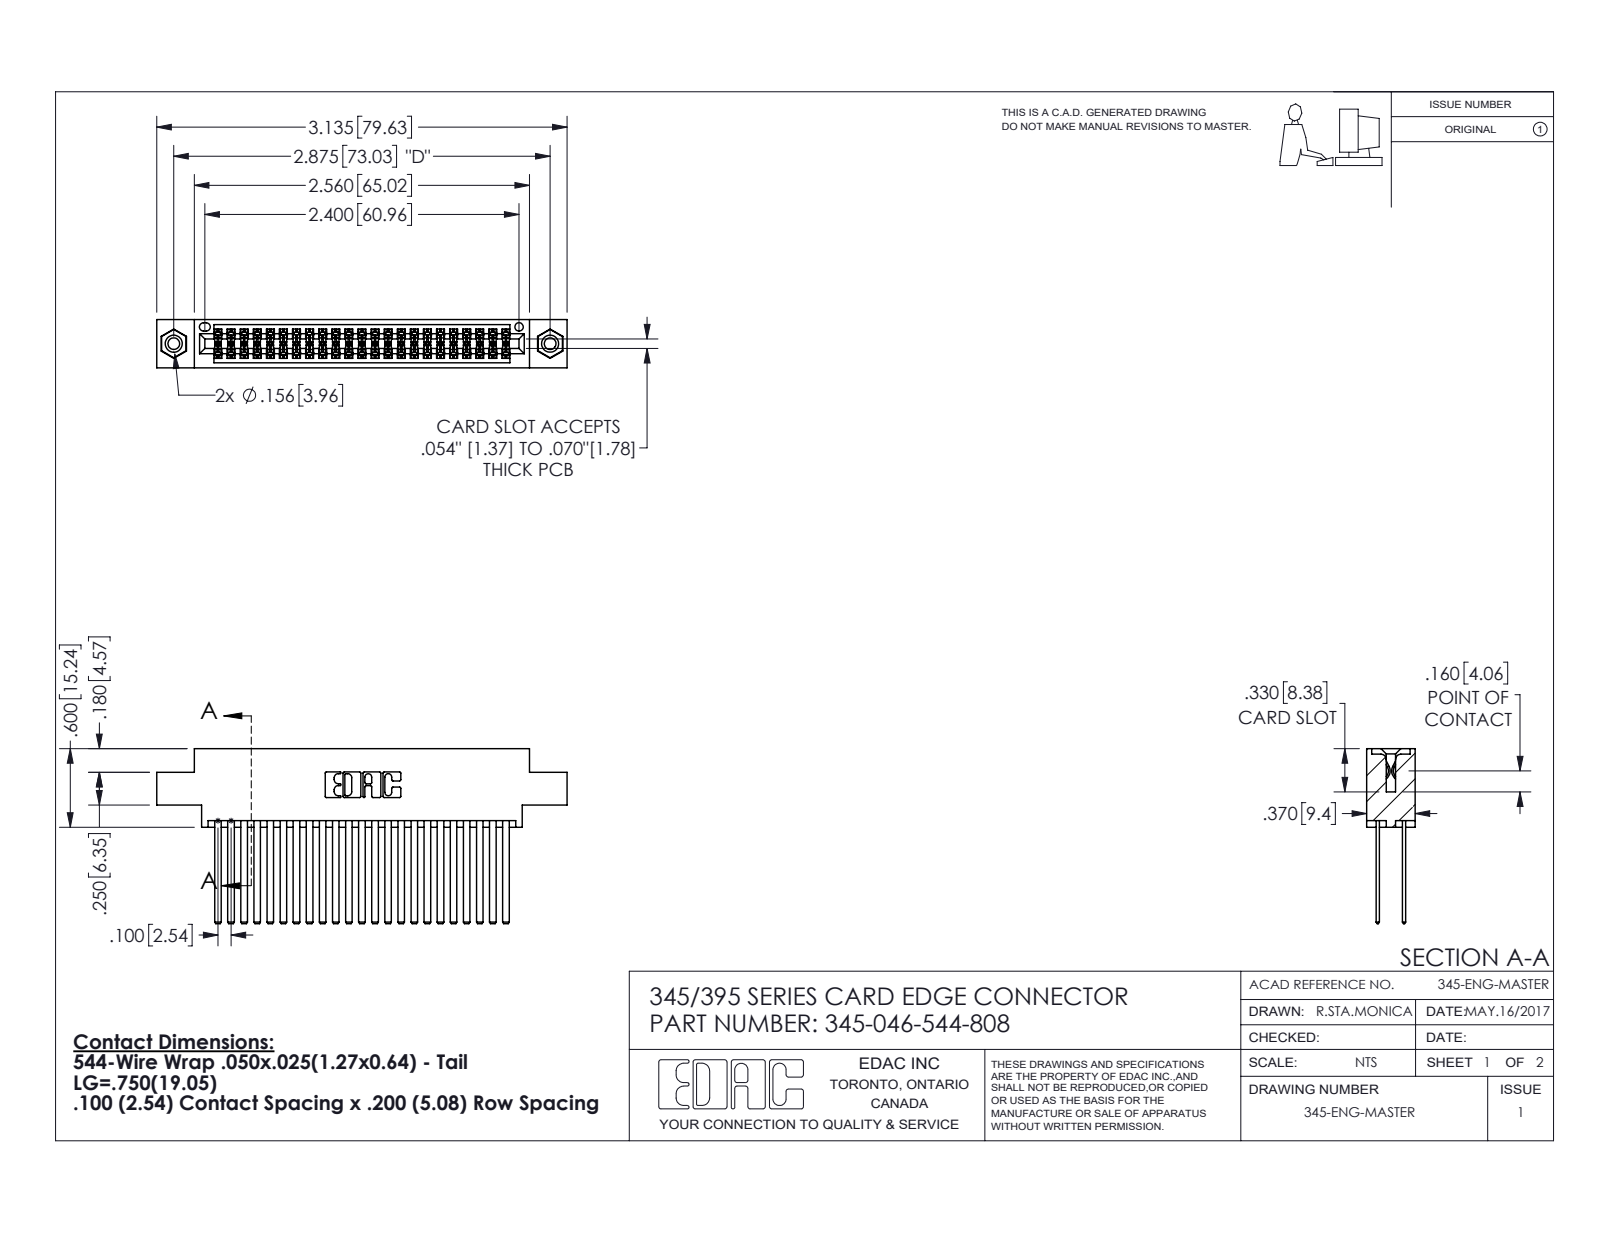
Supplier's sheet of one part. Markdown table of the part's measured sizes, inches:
| quantity | value |
| --- | --- |
| part name | 345-046-544-808; 345-250-001_345-250-003-102; 345 Part_0.170 Offset - 0.156 Dia-TI; 345-292-001_345-293-144 |
| STEP written by | SolidWorks 2016 (CONFIG_CONTROL_DESIGN) |
| units | inches |
| bodies | 49 solids, 2214 faces (1450 planar, 748 cylindrical, 16 other) |
| overall size | 3.135 × 1.337 × 0.37 |
| volume | 0.493 in³ |
| surface area | 21.12 in² |
| round holes (diameter × count) | 0.089 × 2, 0.125 × 2, 0.156 × 2, 0.064 × 1 |
| round bosses / shafts (diameter × count) | 0.155 × 2 |
| partial cylindrical surfaces (radius × count) | 0.006 × 69, 0.01 × 22, 0.007 × 6, 0.031 × 6, 0.026 × 3, 0.014 × 2, 0.019 × 2, 0.022 × 2 |
| main face-to-face distances | 0.2, 0.072, 0.298, 0.025, 0.098, 0.272, 0.225, 0.37, 0.175, 0.15 |
| hole center spacings | 0.27, 2.641, 2.875 |
